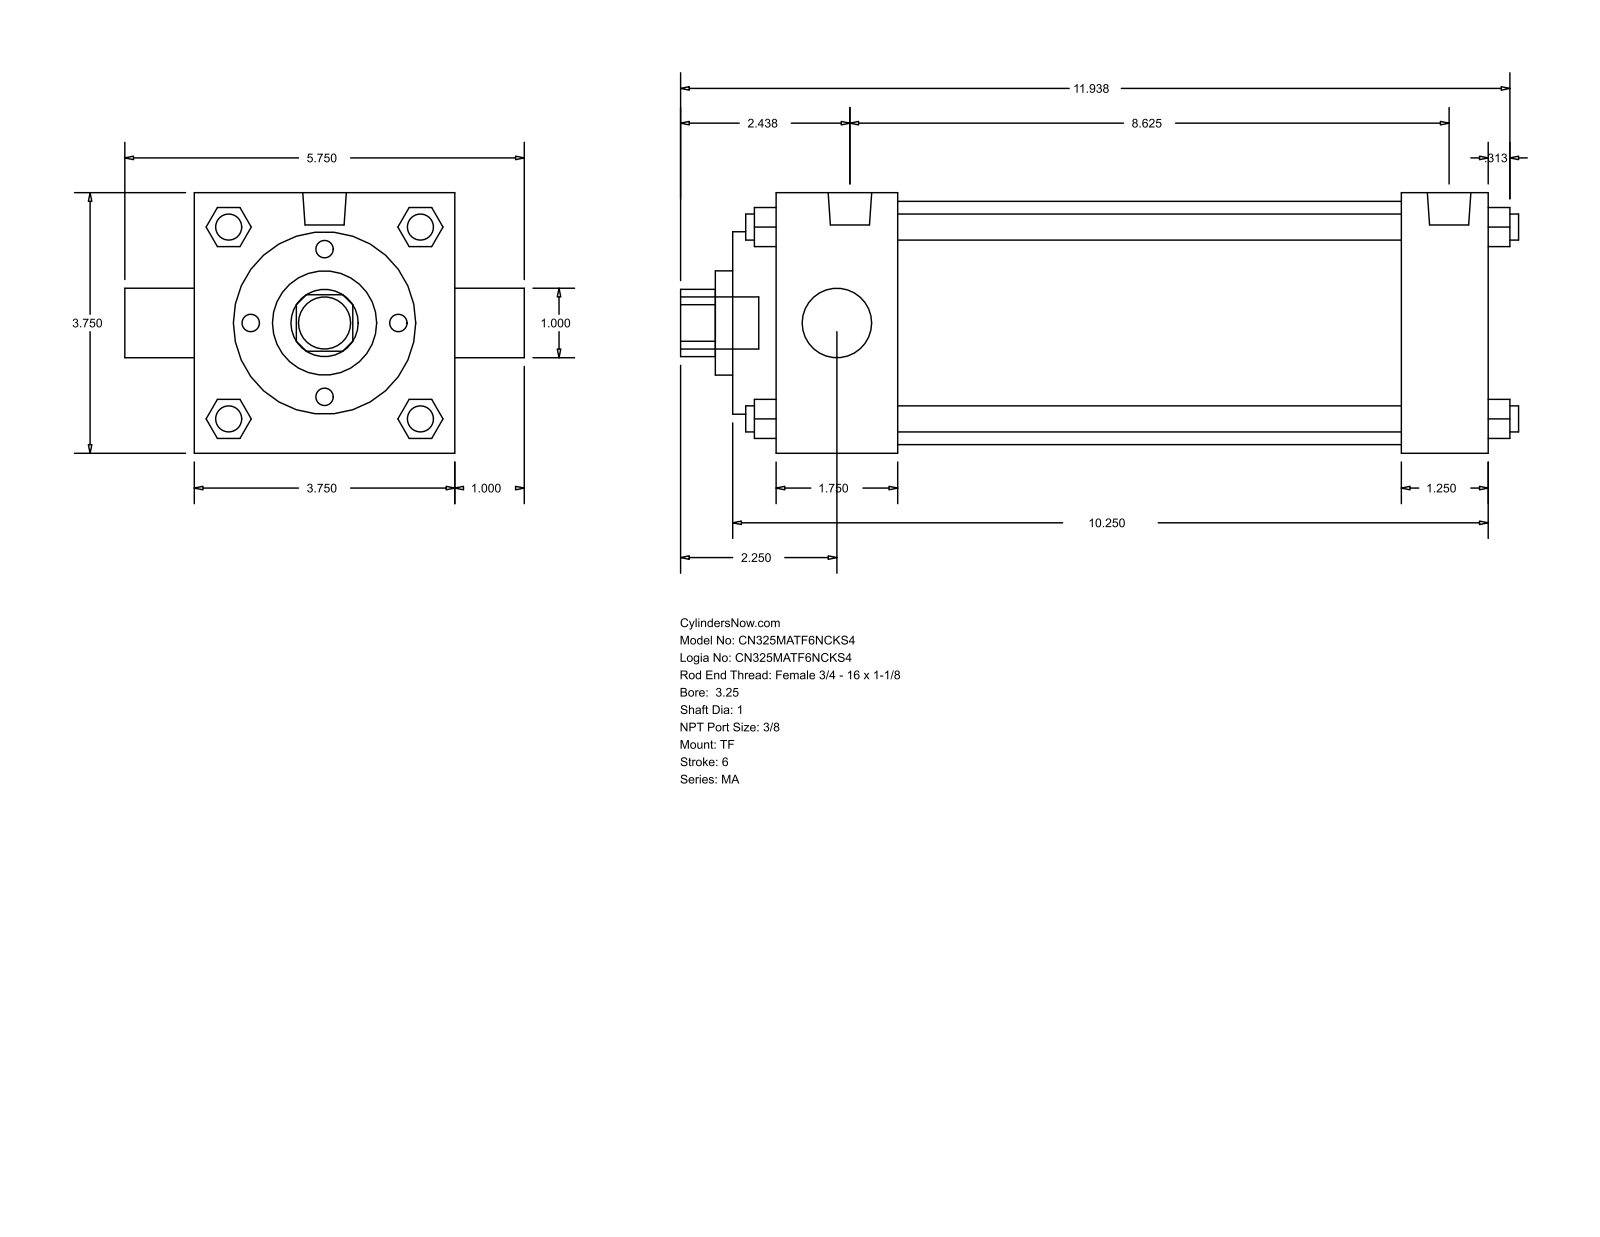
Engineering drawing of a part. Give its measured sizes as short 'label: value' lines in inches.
name: MA_TF__0325_1
written by: GSSL Pune (CONFIG_CONTROL_DESIGN)
unit: in
bodies: 0 solids, 122 faces (93 planar, 29 cylindrical, 0 other)
size: 12.063 × 5.75 × 3.75
holes: 2× ⌀1, 1× ⌀1.5, 1× ⌀2.625, 1× ⌀3.5
bosses: 4× ⌀0.375, 3× ⌀0.437, 2× ⌀0.627, 1× ⌀0.75
rounds: 1× R0.484
face distances: 3.75, 10.25, 10.875, 0.625, 1.75, 9, 7.25, 8.5, 1.25, 2.375
